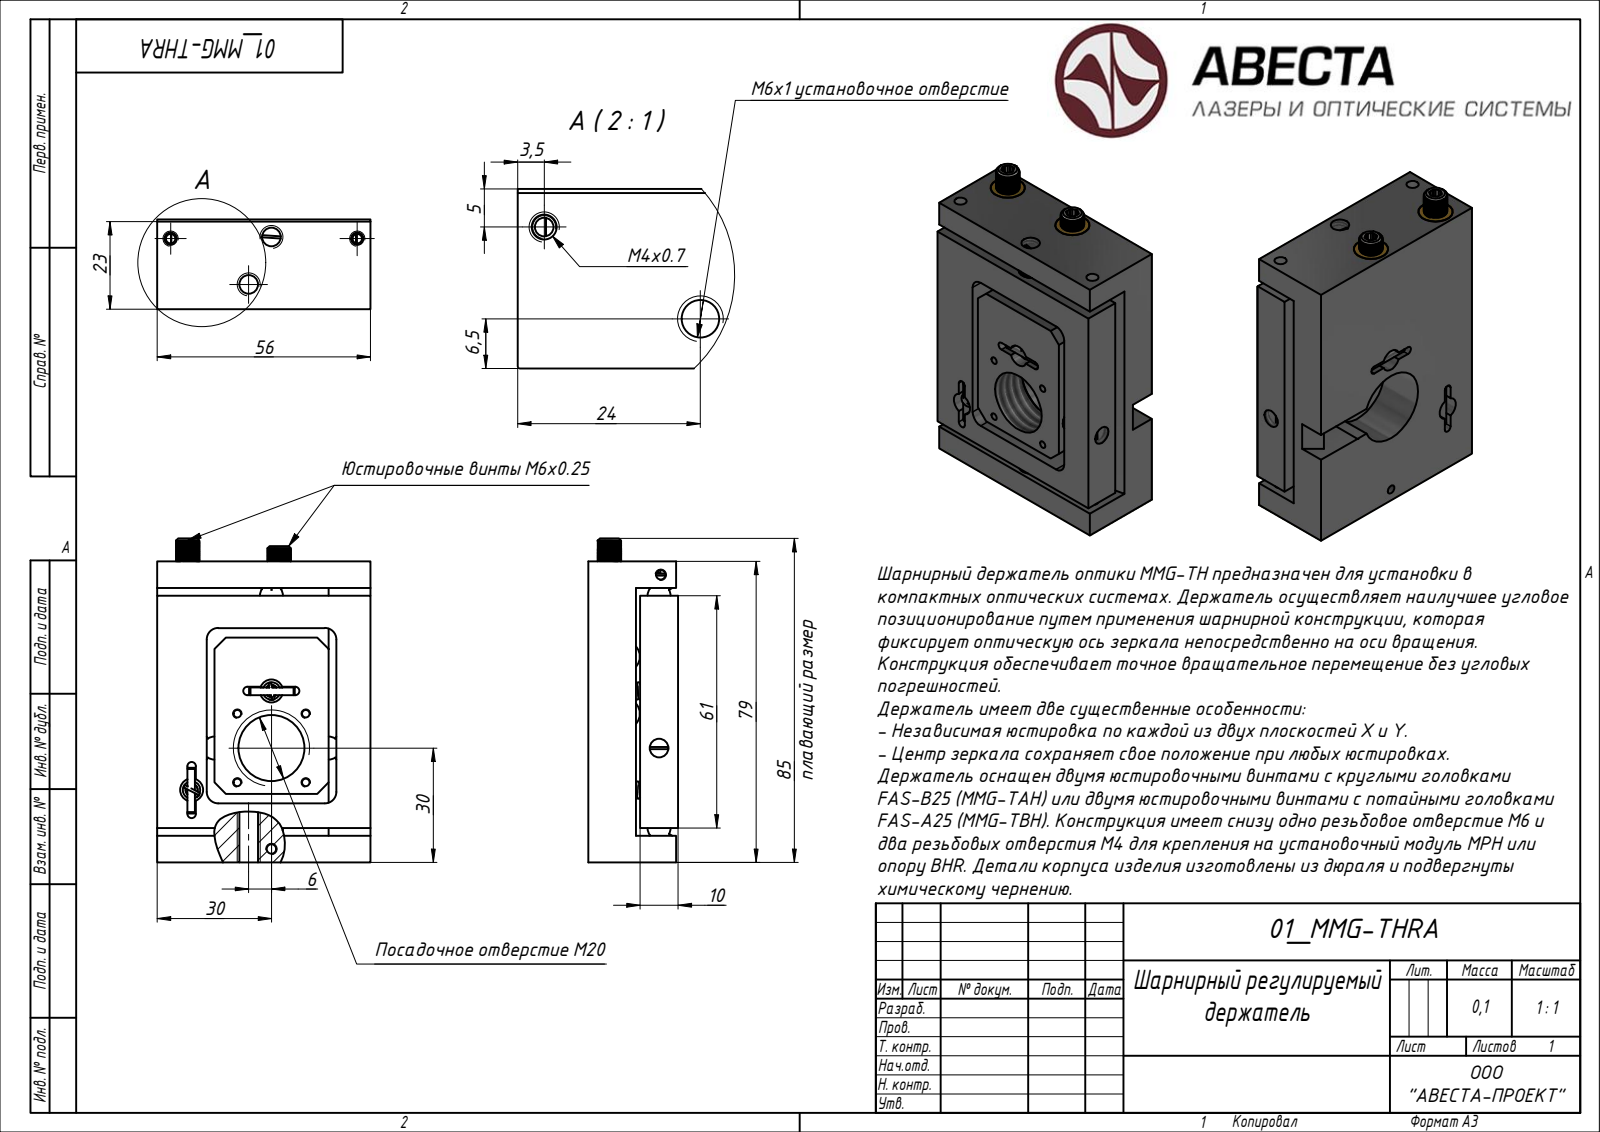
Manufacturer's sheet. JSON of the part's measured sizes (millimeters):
{"step_written_by": "ST-DEVELOPER v15 (AUTOMOTIVE_DESIGN)", "units": "millimeters", "bodies": {"solids": 23, "faces": 428, "planar": 154, "cylindrical": 0, "other": 274}, "overall_size": [82.22, 56, 23.56], "volume_mm3": 82487, "surface_area_mm2": 36160, "face_to_face_distances": [23.56, 13.56, 10, 12.5, 11.06, 1.06, 2, 9, 56, 7]}
